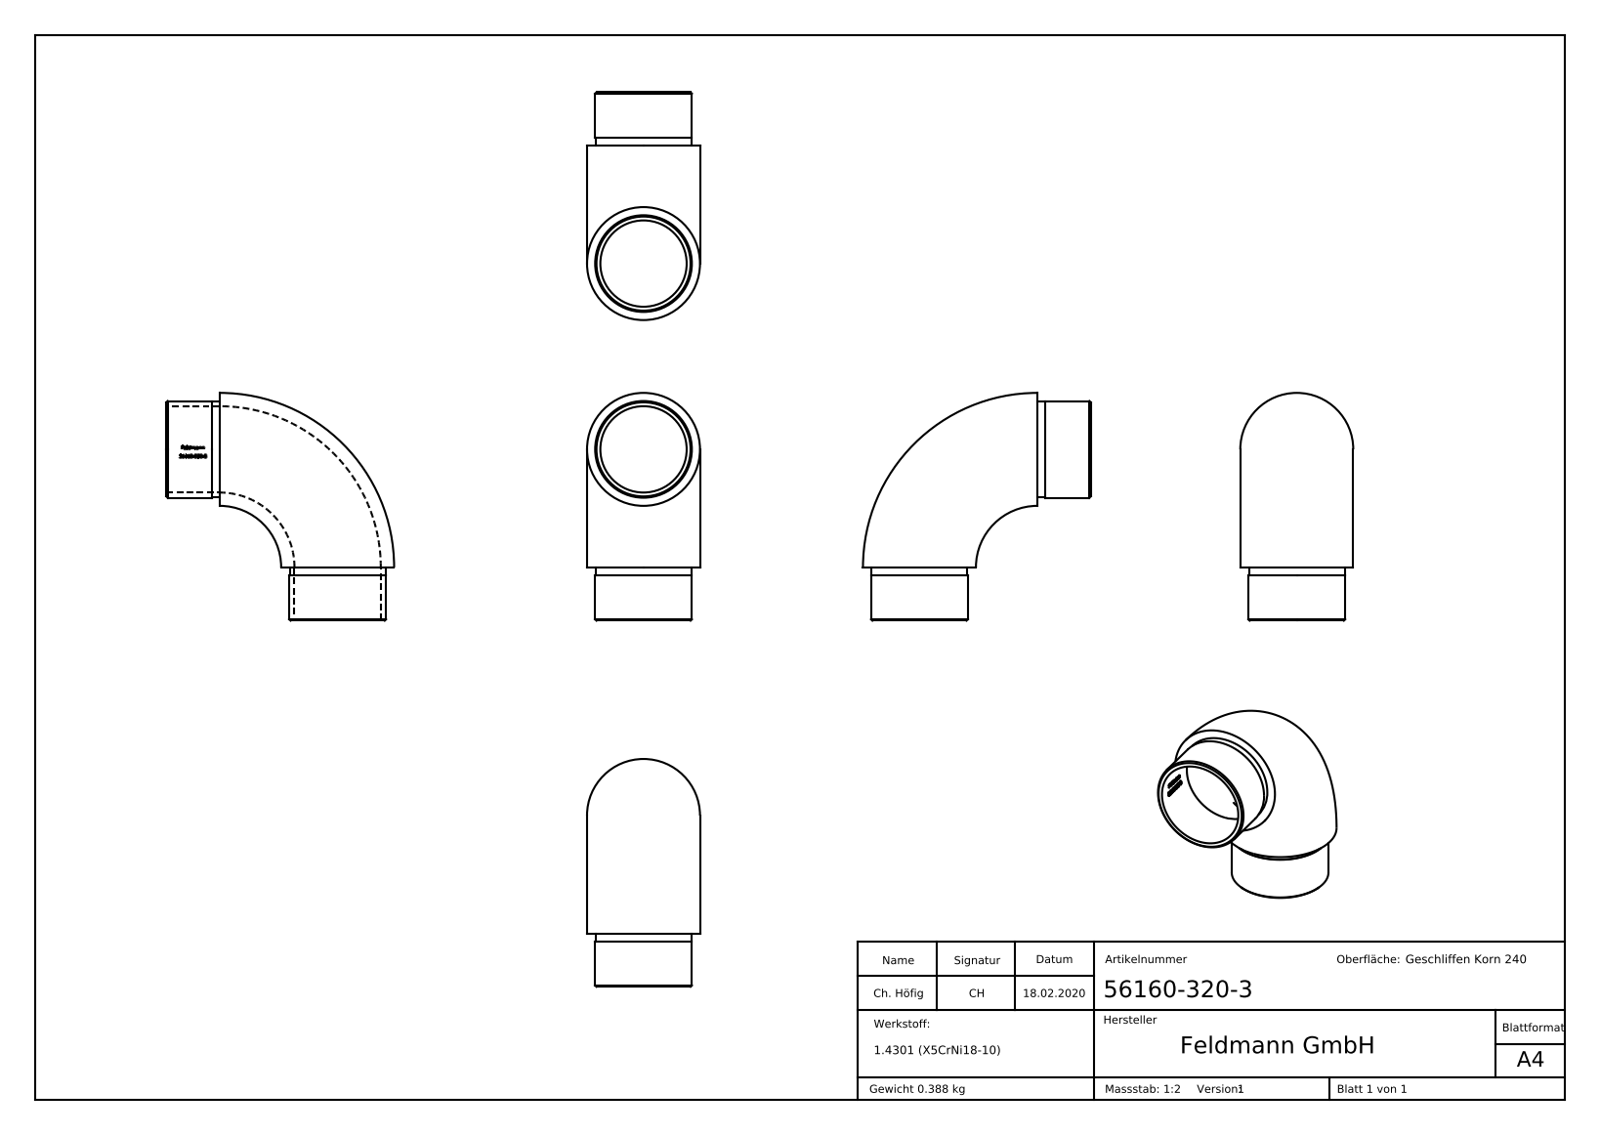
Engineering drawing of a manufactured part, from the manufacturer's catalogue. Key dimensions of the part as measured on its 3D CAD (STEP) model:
Part name (STEP PRODUCT): 56160-320-3
STEP written by: SolidWorks 2015 (CONFIG_CONTROL_DESIGN)
Units: millimetres
Bodies: 1 solid, 260 faces (98 planar, 32 cylindrical, 130 other)
Overall size (bounding box): 85.5 × 85.5 × 42.4
Volume: 49 133 mm³ · Surface area: 26 186 mm²
Round holes (diameter × count): ⌀32.4 ×2
Round bosses / shafts (diameter × count): ⌀36.3 ×2, ⌀35.9 ×2
Partial cylindrical surfaces — rounded edges, fillets, slot ends (radius × count): R16.3 ×1
Main face-to-face distances: 20, 17, 3, 2.97, 0.44, 0.39, 1.32, 3.66, 3.27, 1.58
